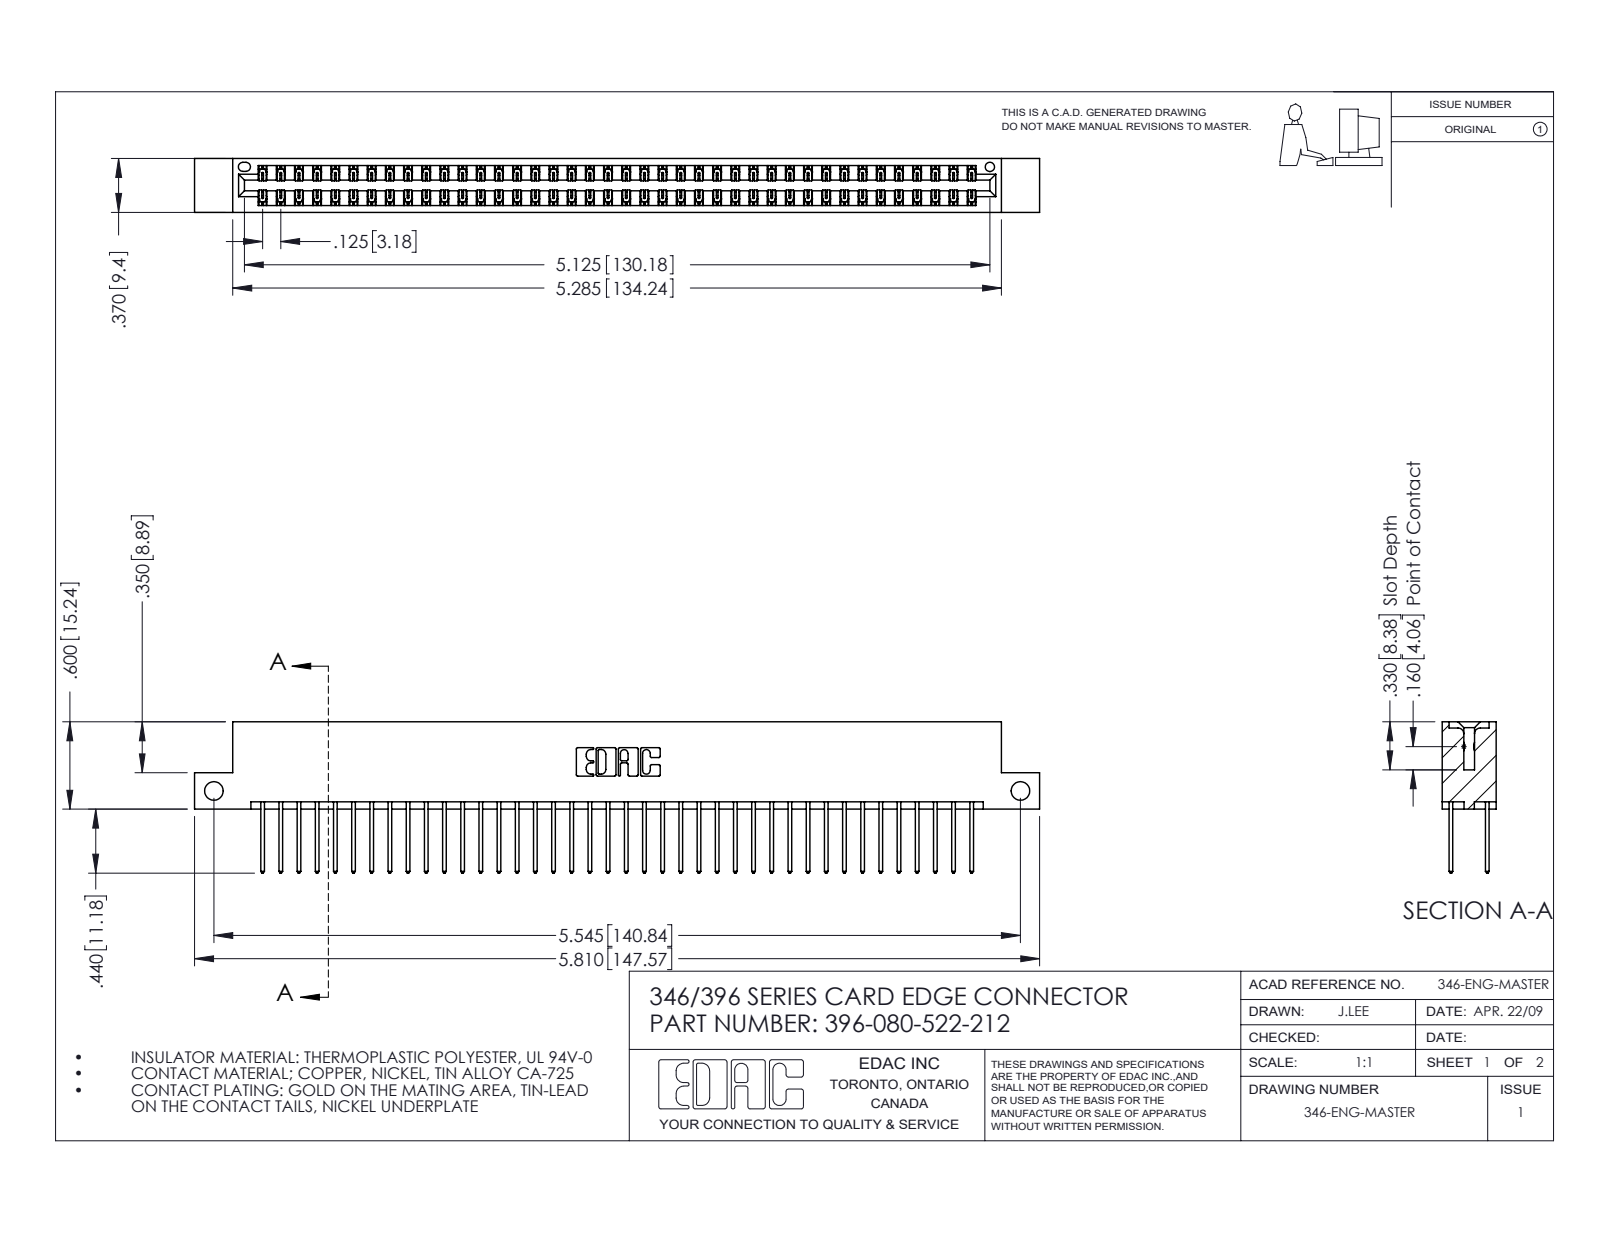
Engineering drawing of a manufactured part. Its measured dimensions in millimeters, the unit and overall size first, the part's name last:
Units: millimetres
Overall size (bounding box): 147.6 × 26.4 × 9.4
Round holes (diameter × count): ⌀3.3 ×2, ⌀1.6 ×1
Partial cylindrical surfaces — rounded edges, fillets, slot ends (radius × count): R0.2 ×120, R0.3 ×80, R0.3 ×22, R0.2 ×6, R0.8 ×6, R0.7 ×3, R0.4 ×2, R0.6 ×2
Main face-to-face distances: 1.2, 8.2, 6.4, 9.4, 1.8, 7.6, 0.6, 7, 3.8, 5.6
Hole centre spacings: 140.8
Volume: 14 500 mm³ · Surface area: 20 700 mm²
Bodies: 81 solids, 4282 faces (2876 planar, 1406 cylindrical, 0 other)
Part name (STEP PRODUCT): 396-080-522-212; 346 Part_Flush Mounting Lugs - Side Mount; 345-292-001_345-293-122
STEP written by: SolidWorks 2016 (CONFIG_CONTROL_DESIGN)
